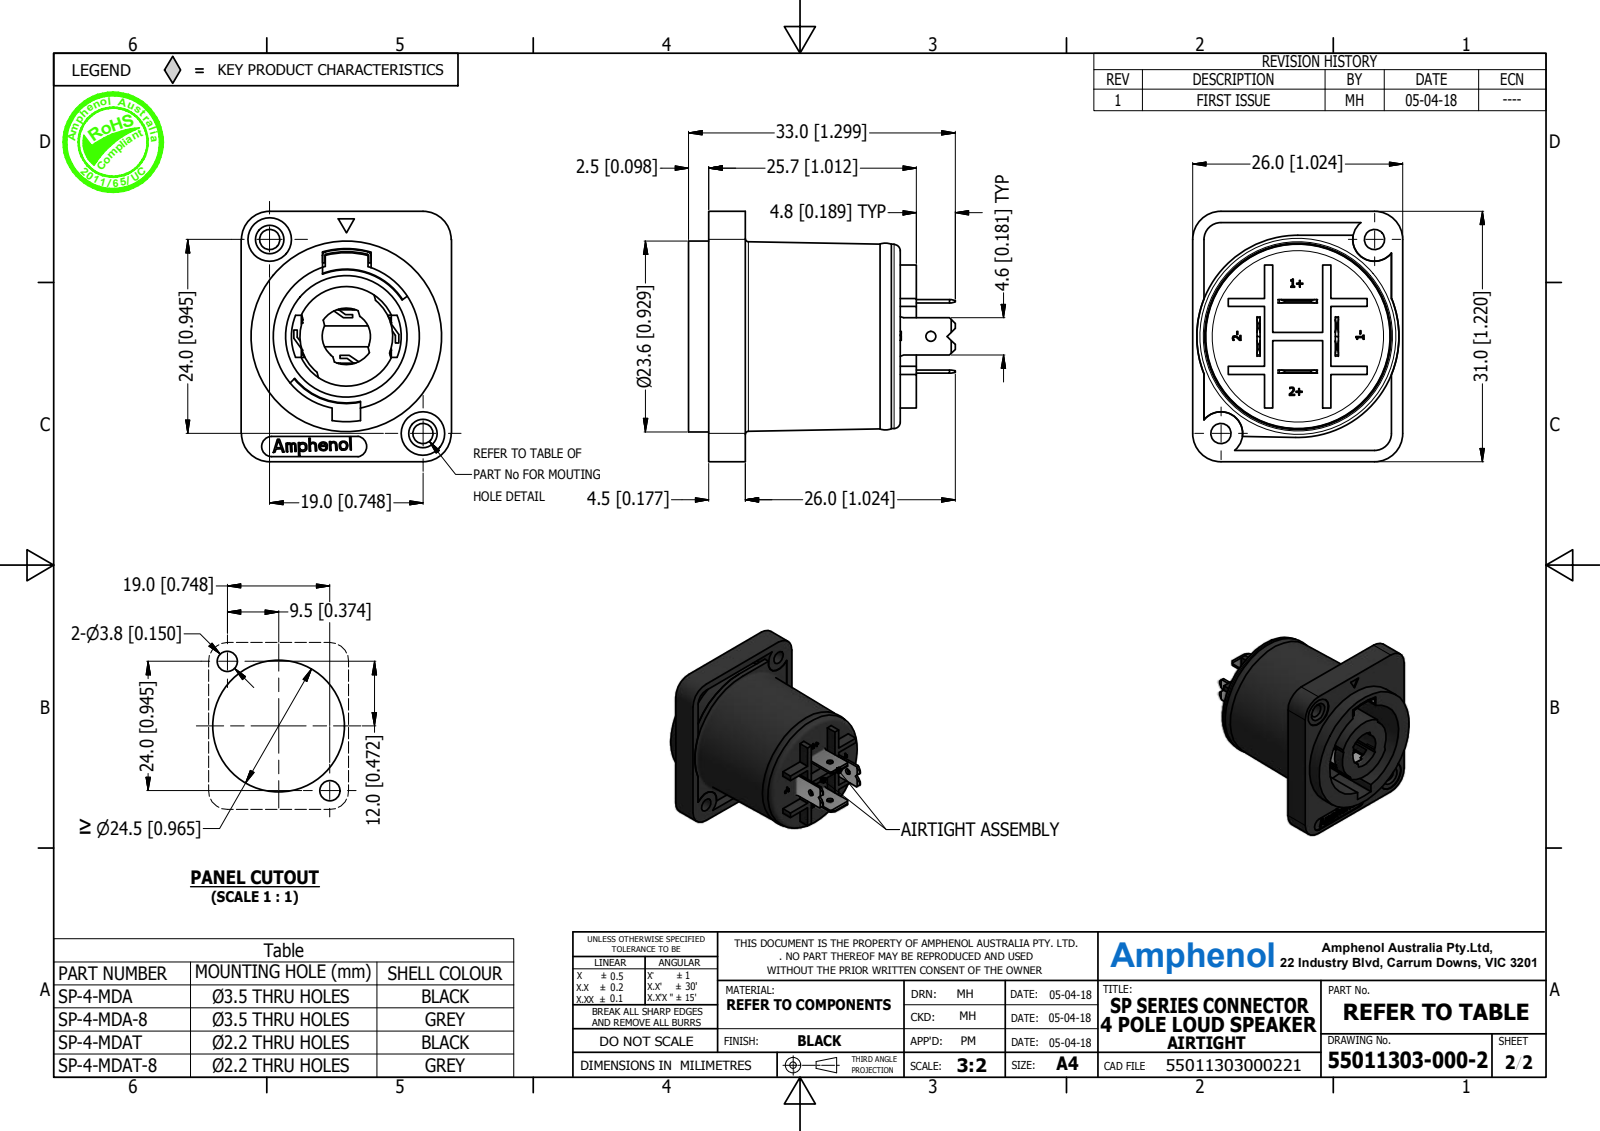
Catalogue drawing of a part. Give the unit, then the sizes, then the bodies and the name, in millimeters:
Units: millimetres
Overall size (bounding box): 37.6 × 36.98 × 33
Round holes (diameter × count): ⌀1.2 ×2, ⌀2.5 ×2, ⌀18.1 ×1
Round bosses / shafts (diameter × count): ⌀25 ×1, ⌀23.6 ×1
Partial cylindrical surfaces — rounded edges, fillets, slot ends (radius × count): R0.6 ×8, R3.5 ×5, R0.2 ×2, R2.1 ×2, R2.7 ×2, R3.02 ×2, R0.25 ×1, R1.25 ×1
Main face-to-face distances: 20.15, 1.4, 18.05, 23.7, 22.55, 1.15, 4.5, 26.2, 2.5, 25.05
Hole centre spacings: 15.31, 30.61
Bodies: 0 solids, 250 faces (195 planar, 47 cylindrical, 8 other)
Part name (STEP PRODUCT): SP-4-MDAT_Shrinkwrap_2
STEP written by: Autodesk Inventor 2016 (AUTOMOTIVE_DESIGN)
